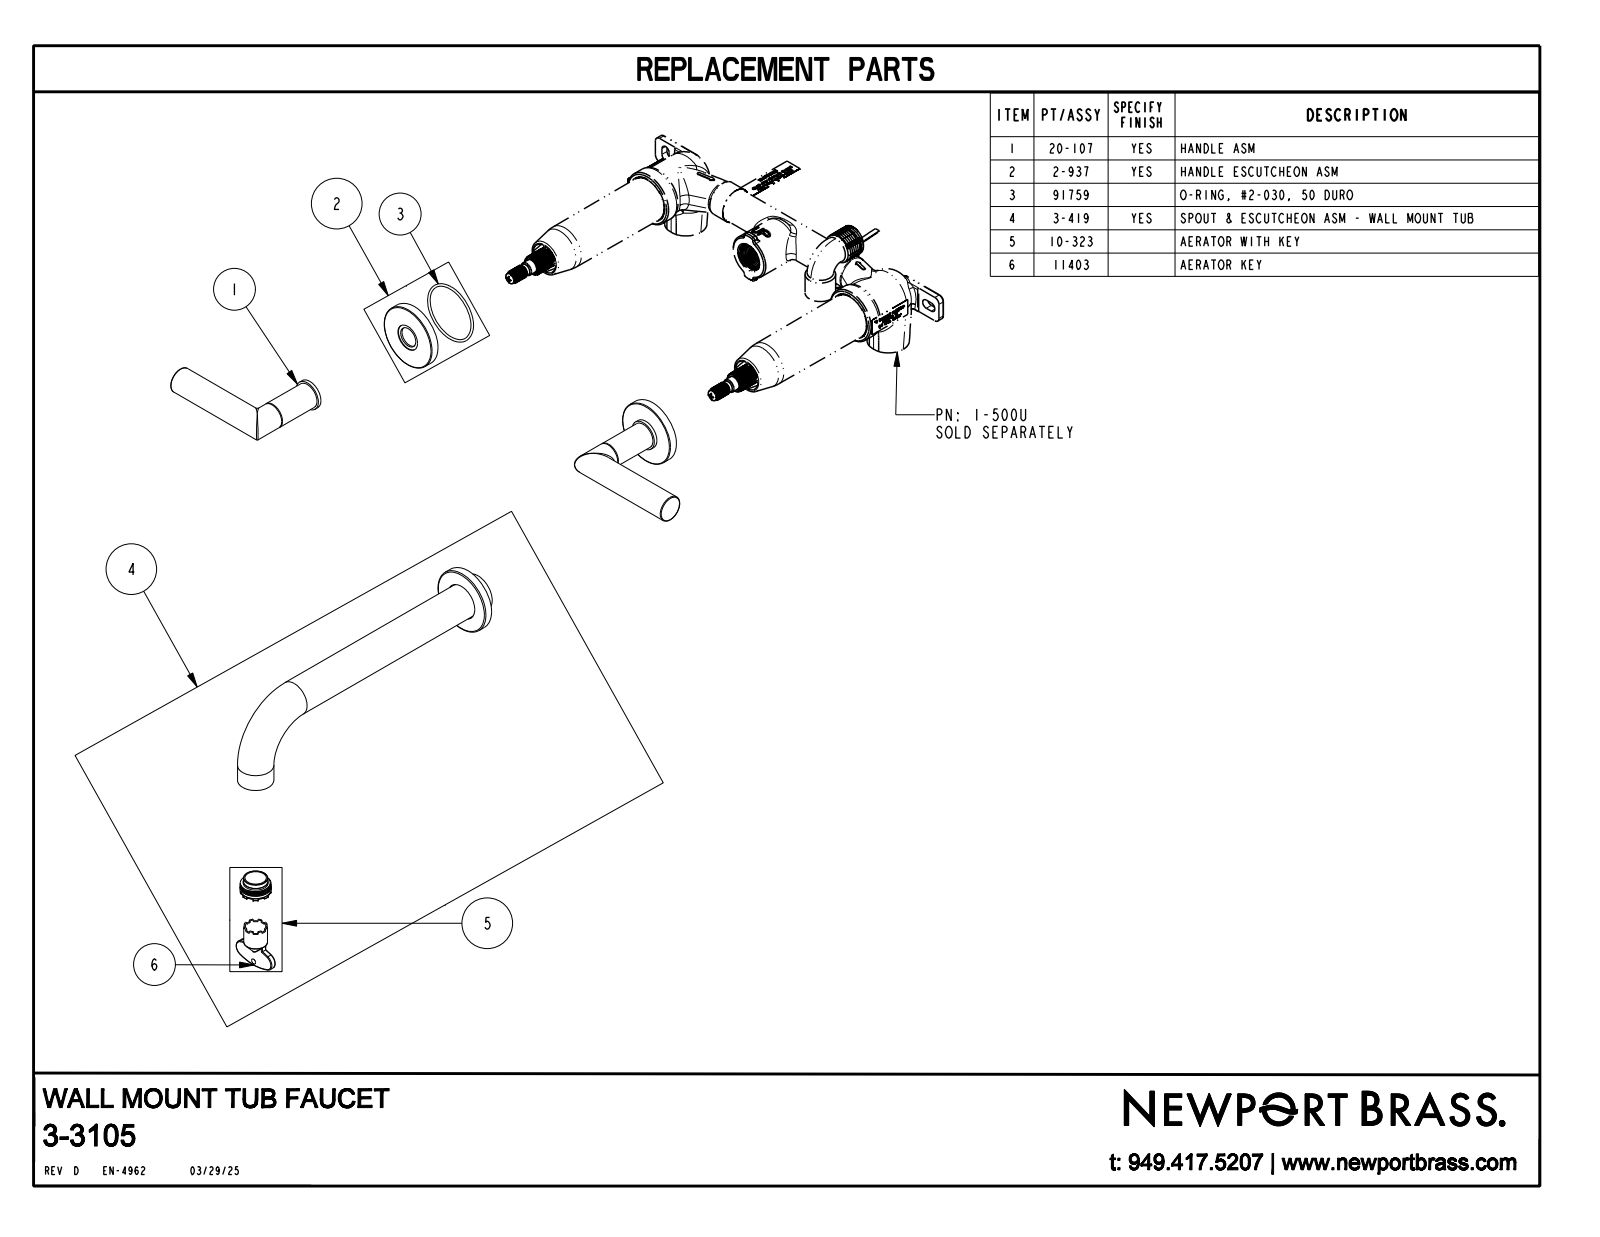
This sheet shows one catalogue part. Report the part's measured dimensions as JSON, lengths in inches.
{"part_name": "3-3105_SW0001", "step_written_by": "CREO PARAMETRIC BY PTC INC, 2018400 (AUTOMOTIVE_DESIGN)", "units": "inches", "bodies": {"solids": 5, "faces": 67, "planar": 17, "cylindrical": 30, "other": 20}, "overall_size": [13.875, 8.925, 8.75], "volume_in3": 13.83, "surface_area_in2": 76.72, "round_bosses_or_shafts": [[1.85, 3], [0.75, 3], [1, 2], [0.86, 2], [0.5, 2]], "face_to_face_distances": [0.25, 0.261, 1.701, 1.732, 1.451, 1.482, 1.44, 1.471, 0.031, 13.875]}
